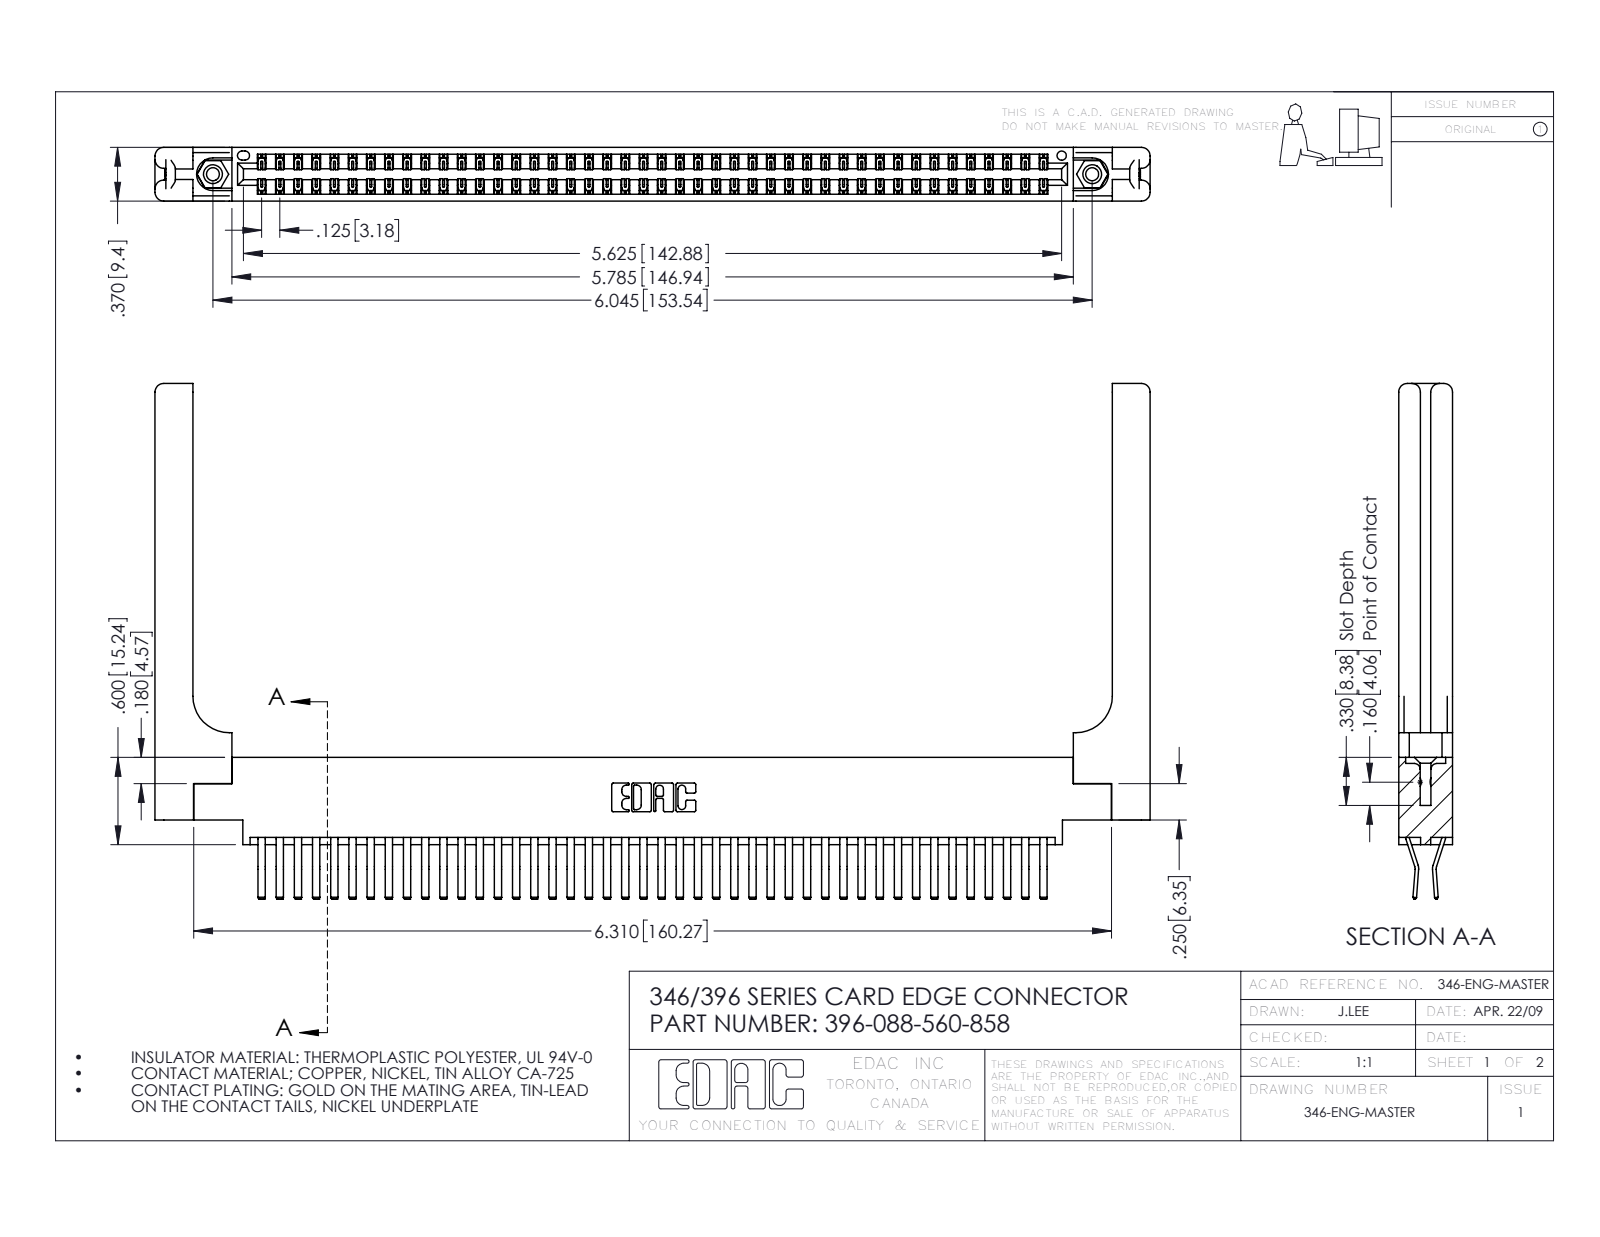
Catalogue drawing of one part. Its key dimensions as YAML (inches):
part_name: "346-220-058_345-220-058; 345-292-001_560 Tail; 396-088-560-858; 345-250-001_345-250-001-102 (+1 more)"
step_written_by: "SolidWorks 2016 (CONFIG_CONTROL_DESIGN)"
units: inches
bodies: {solids: 93, faces: 5134, planar: 3308, cylindrical: 1766, other: 60}
overall_size: [6.841, 3.545, 0.37]
volume: 1.518
surface_area: 47.45
round_holes:
  - {diameter: 0.089, count: 2}
  - {diameter: 0.125, count: 2}
  - {diameter: 0.156, count: 2}
  - {diameter: 0.064, count: 1}
round_bosses_or_shafts:
  - {diameter: 0.155, count: 2}
partial_cylinders:
  - {radius: 0.006, count: 132}
  - {radius: 0.01, count: 22}
  - {radius: 0.06, count: 16}
  - {radius: 0.007, count: 6}
  - {radius: 0.031, count: 6}
  - {radius: 0.026, count: 3}
  - {radius: 0.01, count: 2}
  - {radius: 0.014, count: 2}
face_to_face_distances: [0.37, 0.048, 0.322, 0.072, 0.025, 0.148, 0.15, 0.25, 0.298, 0.275]
hole_center_spacings: [0.246, 5.836, 6.045]
